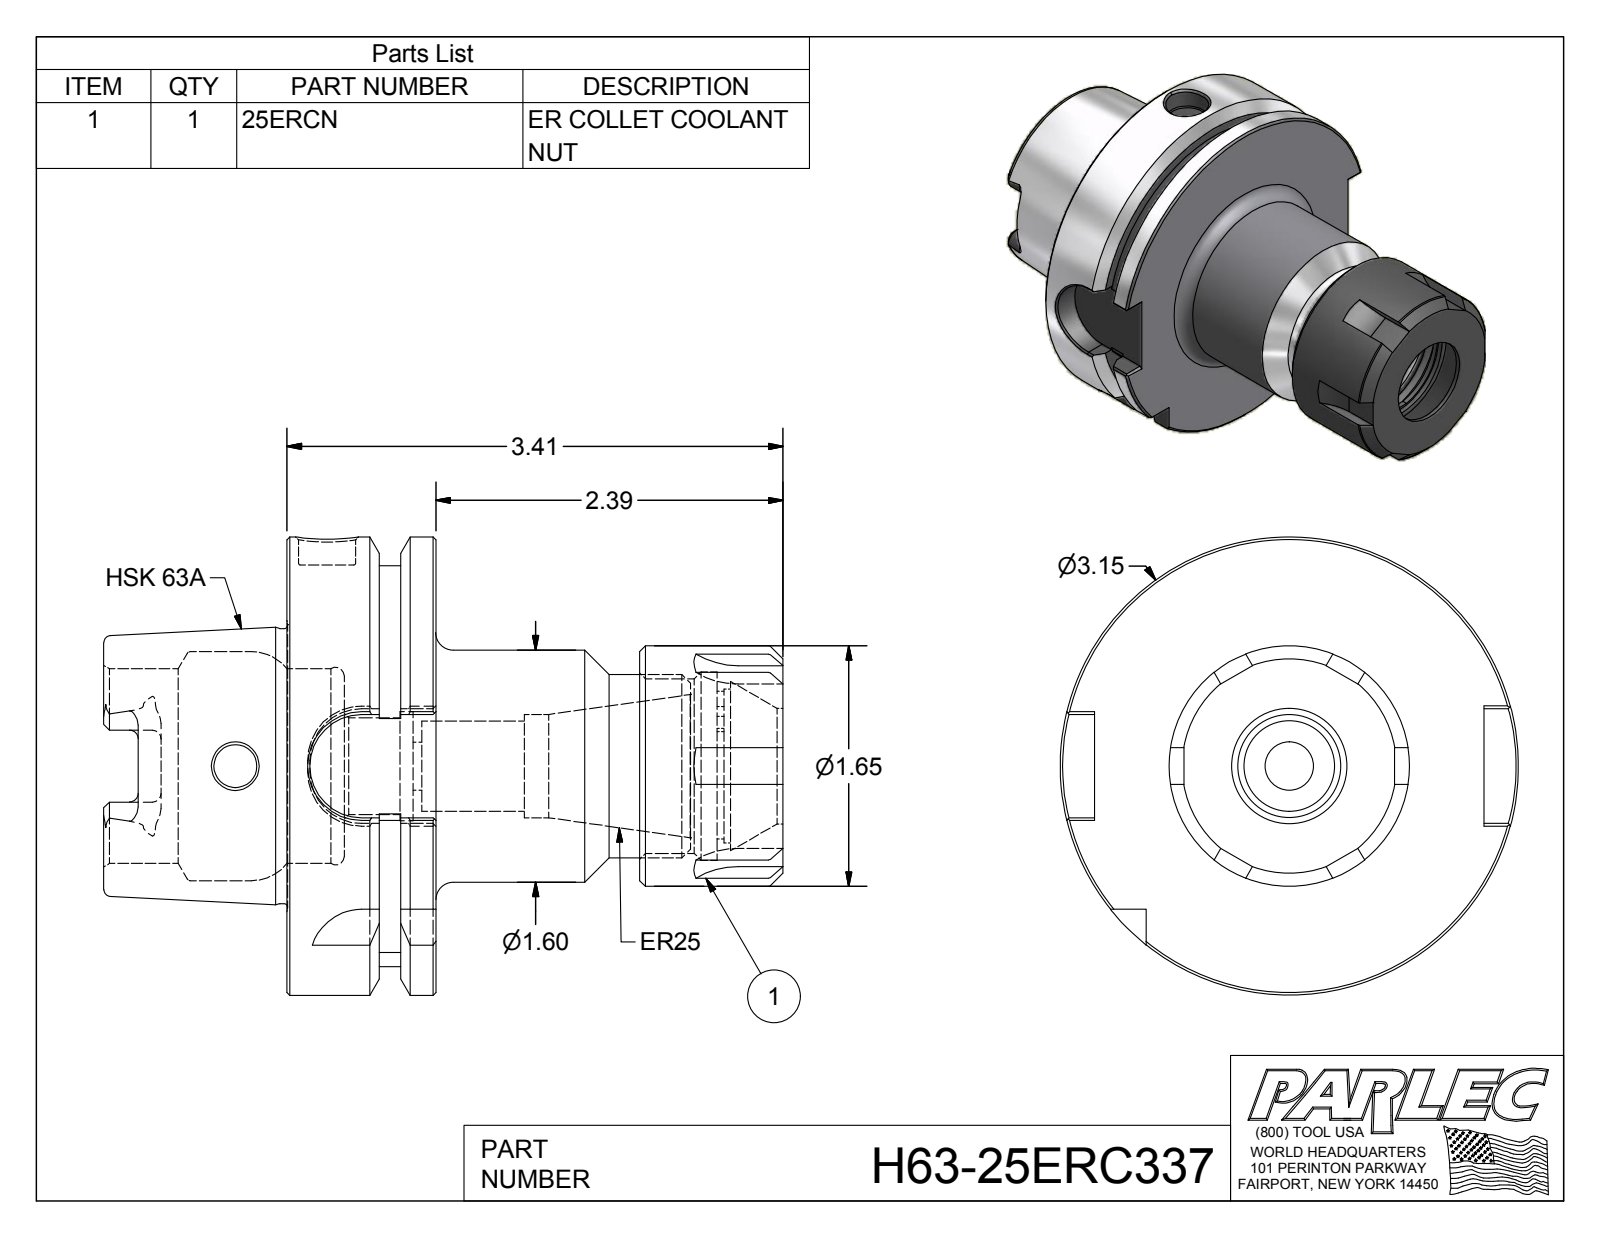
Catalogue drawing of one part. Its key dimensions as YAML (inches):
part_name: "H63-25ERC337; H63-25ER3-1; 25ERCN"
step_written_by: "Autodesk Inventor 2012 (AUTOMOTIVE_DESIGN)"
units: inches
bodies: {solids: 2, faces: 199, planar: 83, cylindrical: 51, other: 65}
overall_size: [4.669, 3.15, 3.15]
volume: 11.03
surface_area: 67.08
round_holes:
  - {diameter: 0.295, count: 1}
  - {diameter: 0.331, count: 1}
  - {diameter: 0.394, count: 1}
  - {diameter: 0.62, count: 1}
  - {diameter: 0.666, count: 1}
  - {diameter: 0.71, count: 1}
  - {diameter: 0.749, count: 1}
  - {diameter: 0.794, count: 1}
  - {diameter: 1.057, count: 1}
  - {diameter: 1.201, count: 1}
  - {diameter: 1.294, count: 1}
  - {diameter: 1.339, count: 1}
round_bosses_or_shafts:
  - {diameter: 3.15, count: 1}
  - {diameter: 1.891, count: 1}
  - {diameter: 1.654, count: 1}
  - {diameter: 1.595, count: 1}
  - {diameter: 1.26, count: 1}
partial_cylinders:
  - {radius: 0.059, count: 6}
  - {radius: 0.5, count: 6}
  - {radius: 0.113, count: 4}
  - {radius: 0.354, count: 4}
  - {radius: 0.472, count: 1}
  - {radius: 0.515, count: 1}
  - {radius: 1.378, count: 1}
face_to_face_distances: [1.024, 0.241, 0.389, 3.409, 2.386, 0.394, 0.63, 3.016, 0.783, 2.627]
